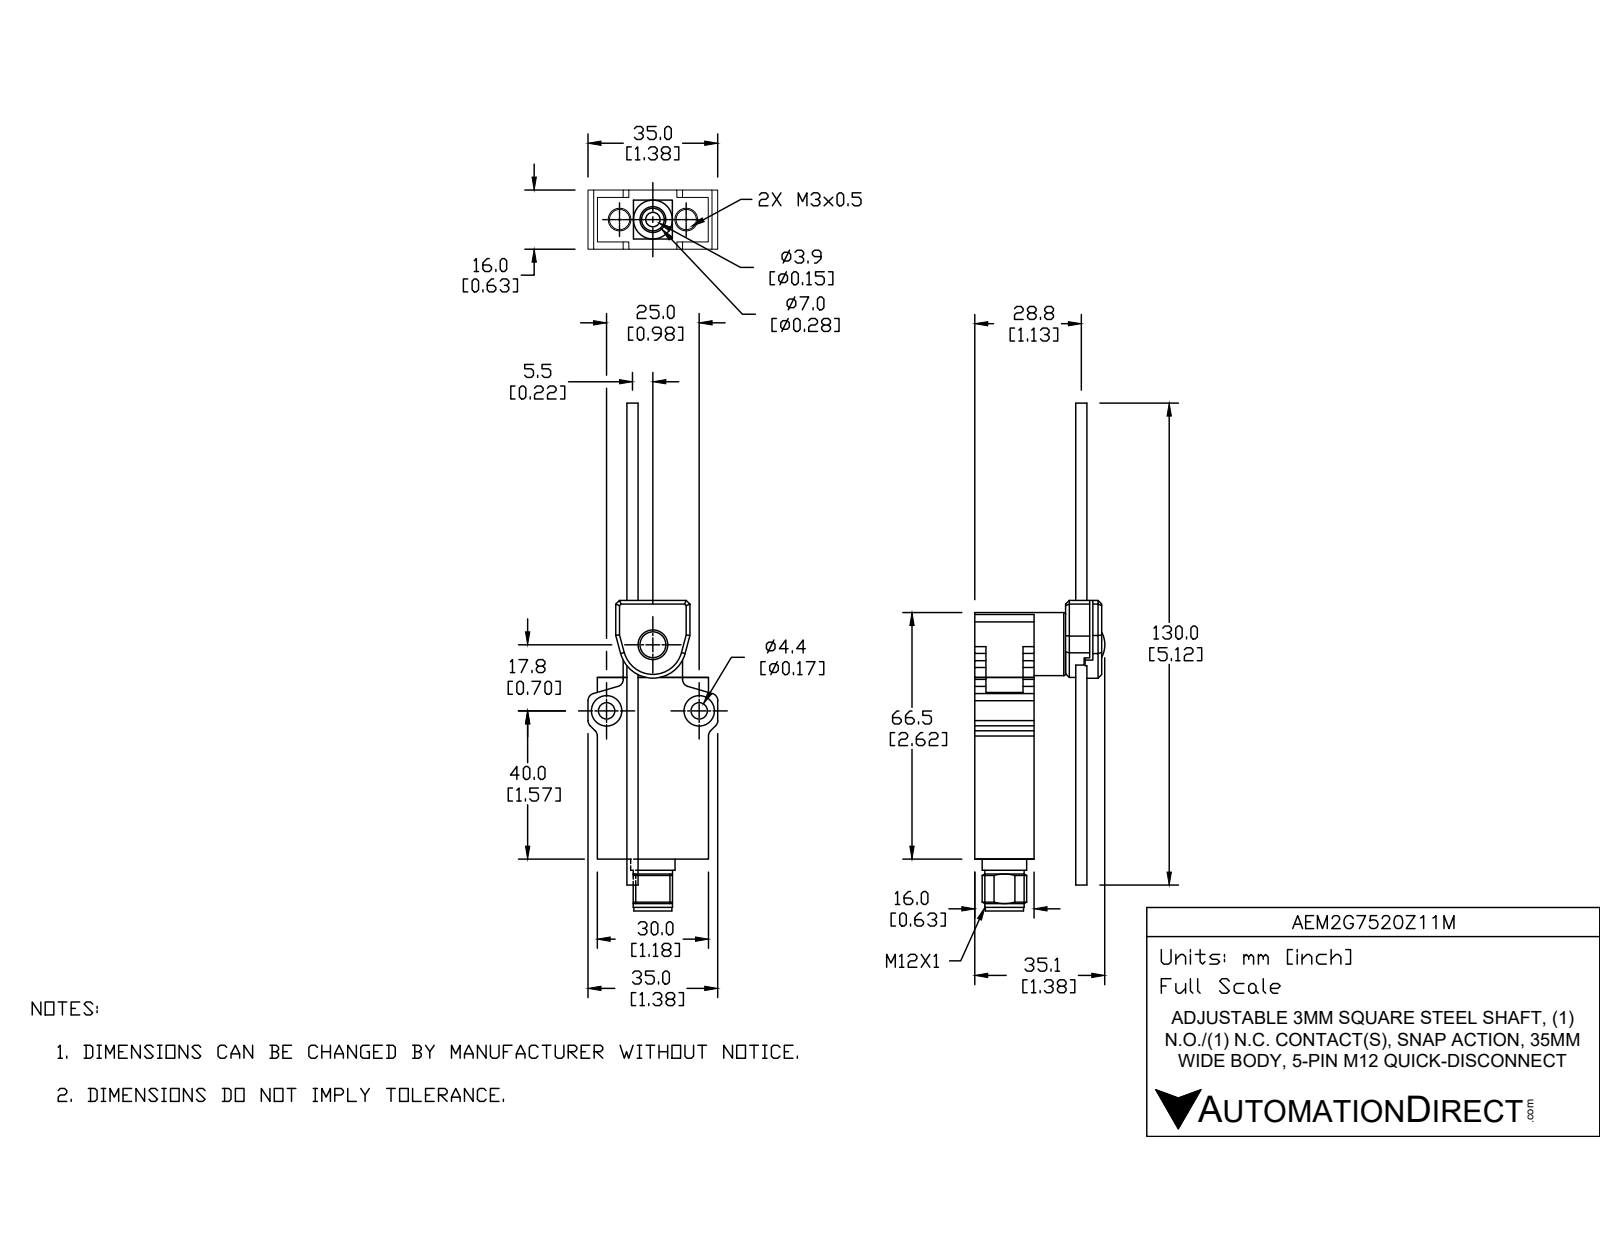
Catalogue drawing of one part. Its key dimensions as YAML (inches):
part_name: "AEM2G7520Z11M"
step_written_by: "SolidWorks 2017 (AUTOMOTIVE_DESIGN)"
units: inches
bodies: {solids: 6, faces: 274, planar: 148, cylindrical: 83, other: 43}
overall_size: [7.045, 1.378, 1.366]
volume: 2.092
surface_area: 21.74
round_holes:
  - {diameter: 0.118, count: 2}
  - {diameter: 0.173, count: 2}
  - {diameter: 0.323, count: 2}
  - {diameter: 0.138, count: 1}
  - {diameter: 0.197, count: 1}
  - {diameter: 0.315, count: 1}
round_bosses_or_shafts:
  - {diameter: 0.622, count: 1}
  - {diameter: 0.472, count: 1}
  - {diameter: 0.417, count: 1}
  - {diameter: 0.406, count: 1}
  - {diameter: 0.276, count: 1}
partial_cylinders:
  - {radius: 0.079, count: 8}
  - {radius: 0.059, count: 2}
  - {radius: 0.173, count: 1}
  - {radius: 0.256, count: 1}
  - {radius: 0.26, count: 1}
  - {radius: 0.354, count: 1}
face_to_face_distances: [0.63, 0.118, 1.181, 0.587, 1.098, 1.217, 0.469, 0.313, 0.868, 0.11]
hole_center_spacings: [0.863, 0.748, 0.984]
